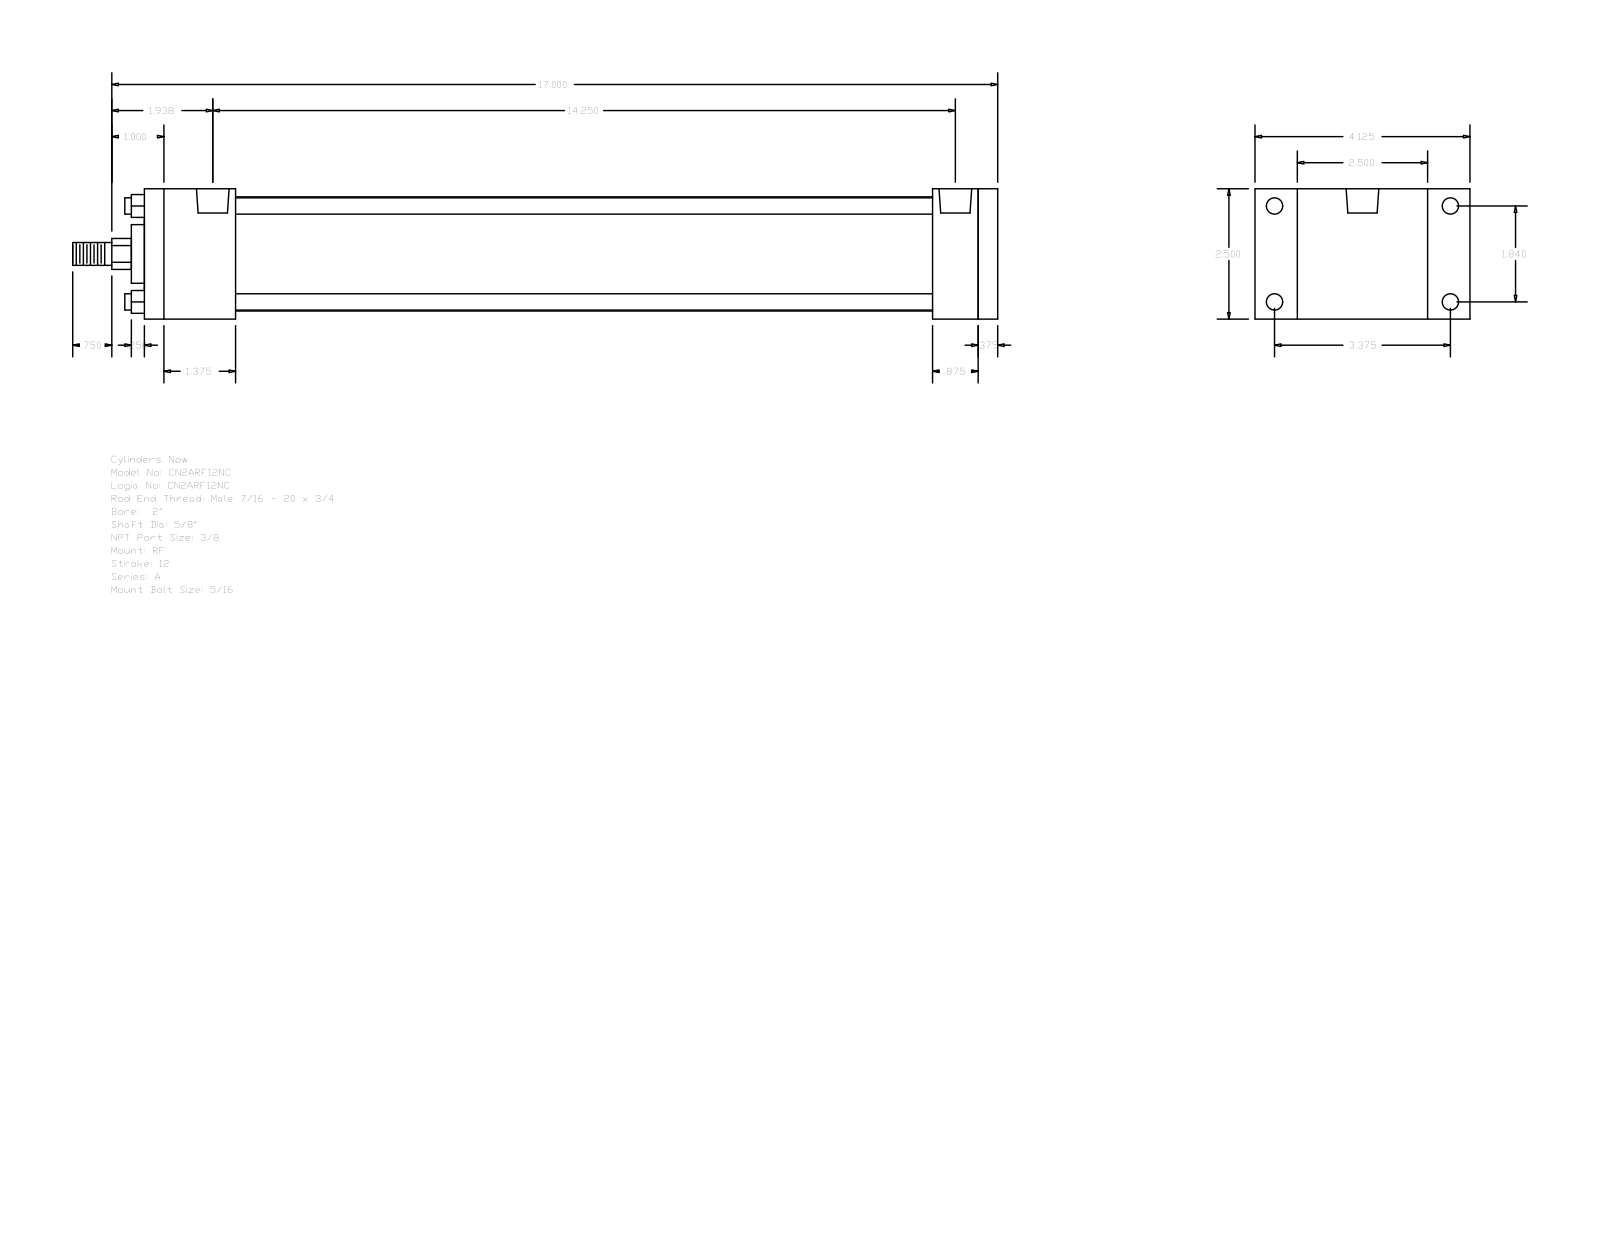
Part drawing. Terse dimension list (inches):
name: A_RF__0200_0.625
written by: GSSL Pune (CONFIG_CONTROL_DESIGN)
unit: in
bodies: 0 solids, 92 faces (64 planar, 28 cylindrical, 0 other)
size: 17.75 × 4.125 × 2.5
holes: 4× ⌀0.219, 4× ⌀0.313, 2× ⌀0.627
bosses: 4× ⌀0.313, 1× ⌀2.19, 1× ⌀1.125, 1× ⌀0.625, 1× ⌀0.437
rounds: 1× R0.297
face distances: 2.5, 16.375, 0.375, 16, 1.75, 14.25, 14.625, 15.125, 13.375, 0.875
hole spacings: 1.84, 3.375, 3.844, 13.937, 0.156, 0.157, 14.093, 14.094
